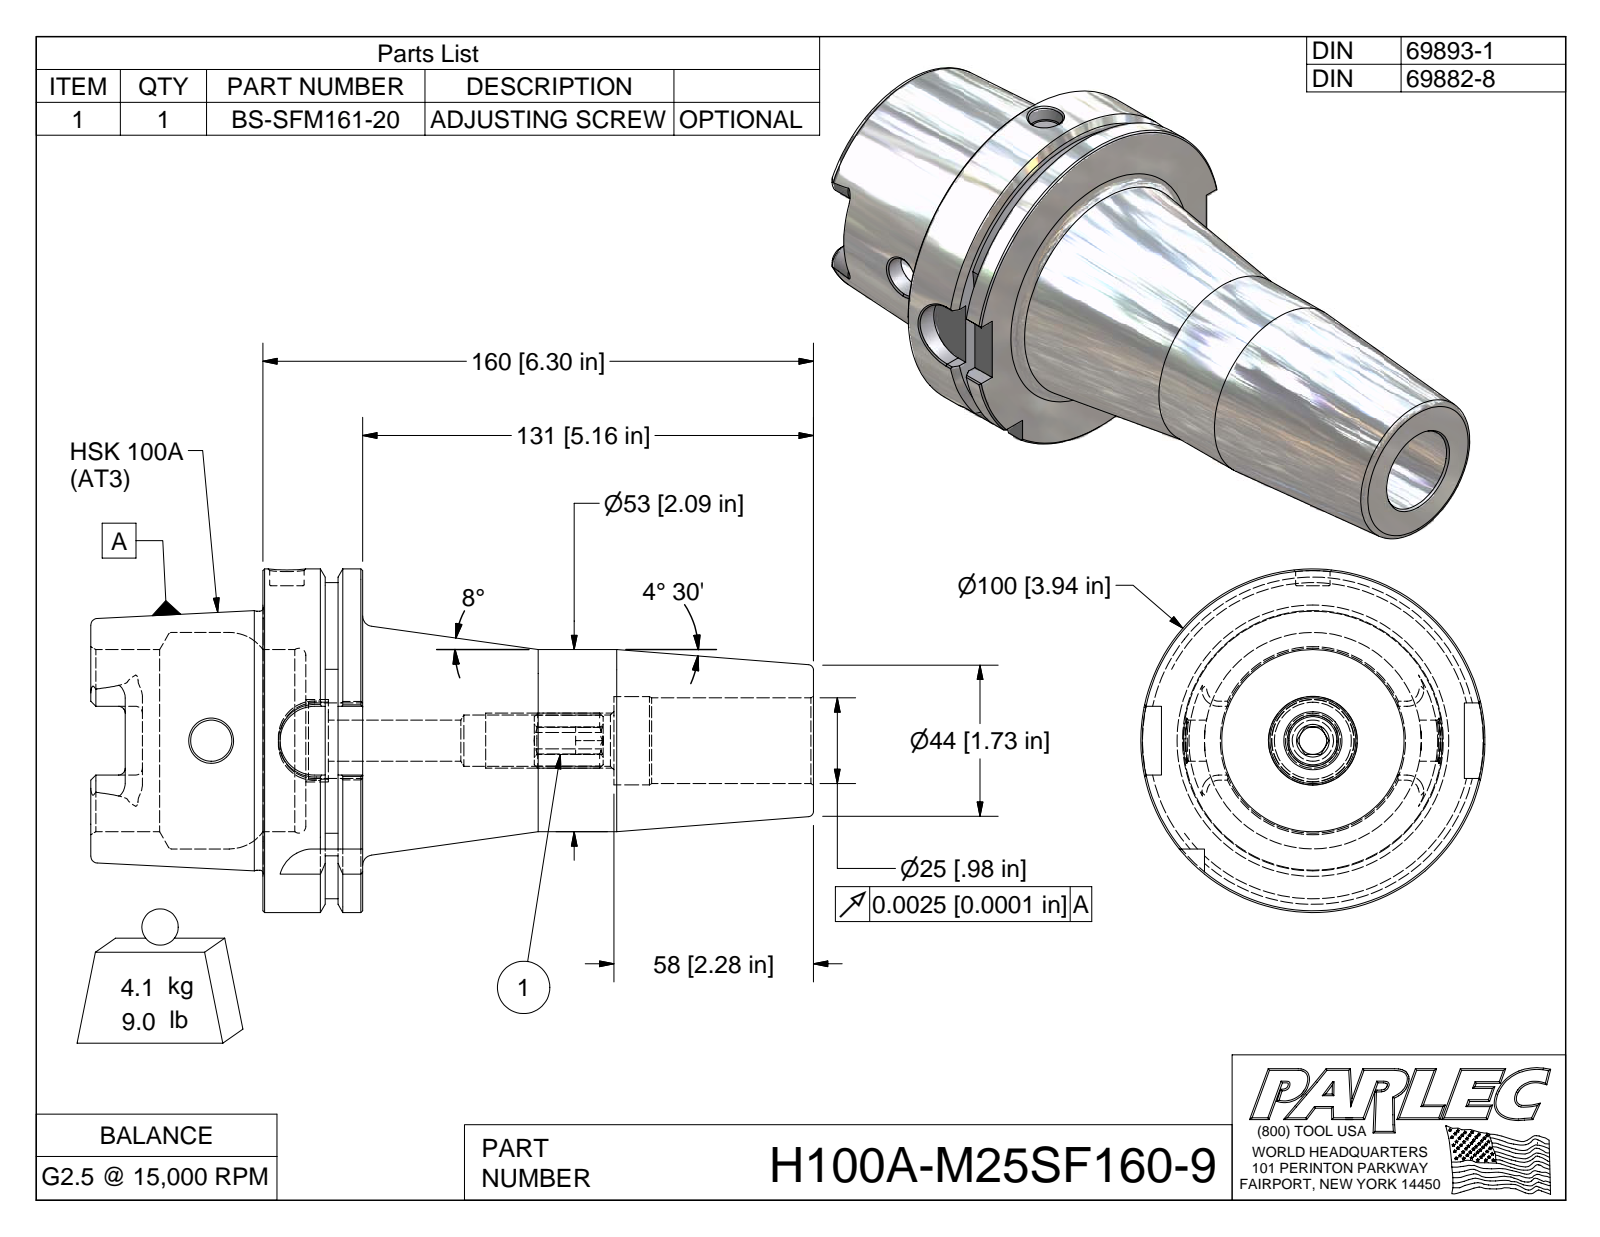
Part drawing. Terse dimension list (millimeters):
name: H100A-M25SF160-9; H100A-M25SF160-9-1; BS-SFM161-20
written by: Autodesk Inventor 2009 (AUTOMOTIVE_DESIGN)
unit: mm
bodies: 2 solids, 148 faces (48 planar, 29 cylindrical, 71 other)
size: 210 × 100 × 100
volume: 521 900 mm³; area: 78 710 mm²
holes: 1× ⌀10, 1× ⌀12, 1× ⌀22.4, 1× ⌀25, 1× ⌀25.7, 1× ⌀53, 1× ⌀63
bosses: 1× ⌀100, 1× ⌀75.4
rounds: 4× R10, 3× R2, 2× R4.9, 1× R8, 1× R46
face distances: 29, 12.5, 16.5, 50, 62.5, 79, 210, 160, 147.5, 131
